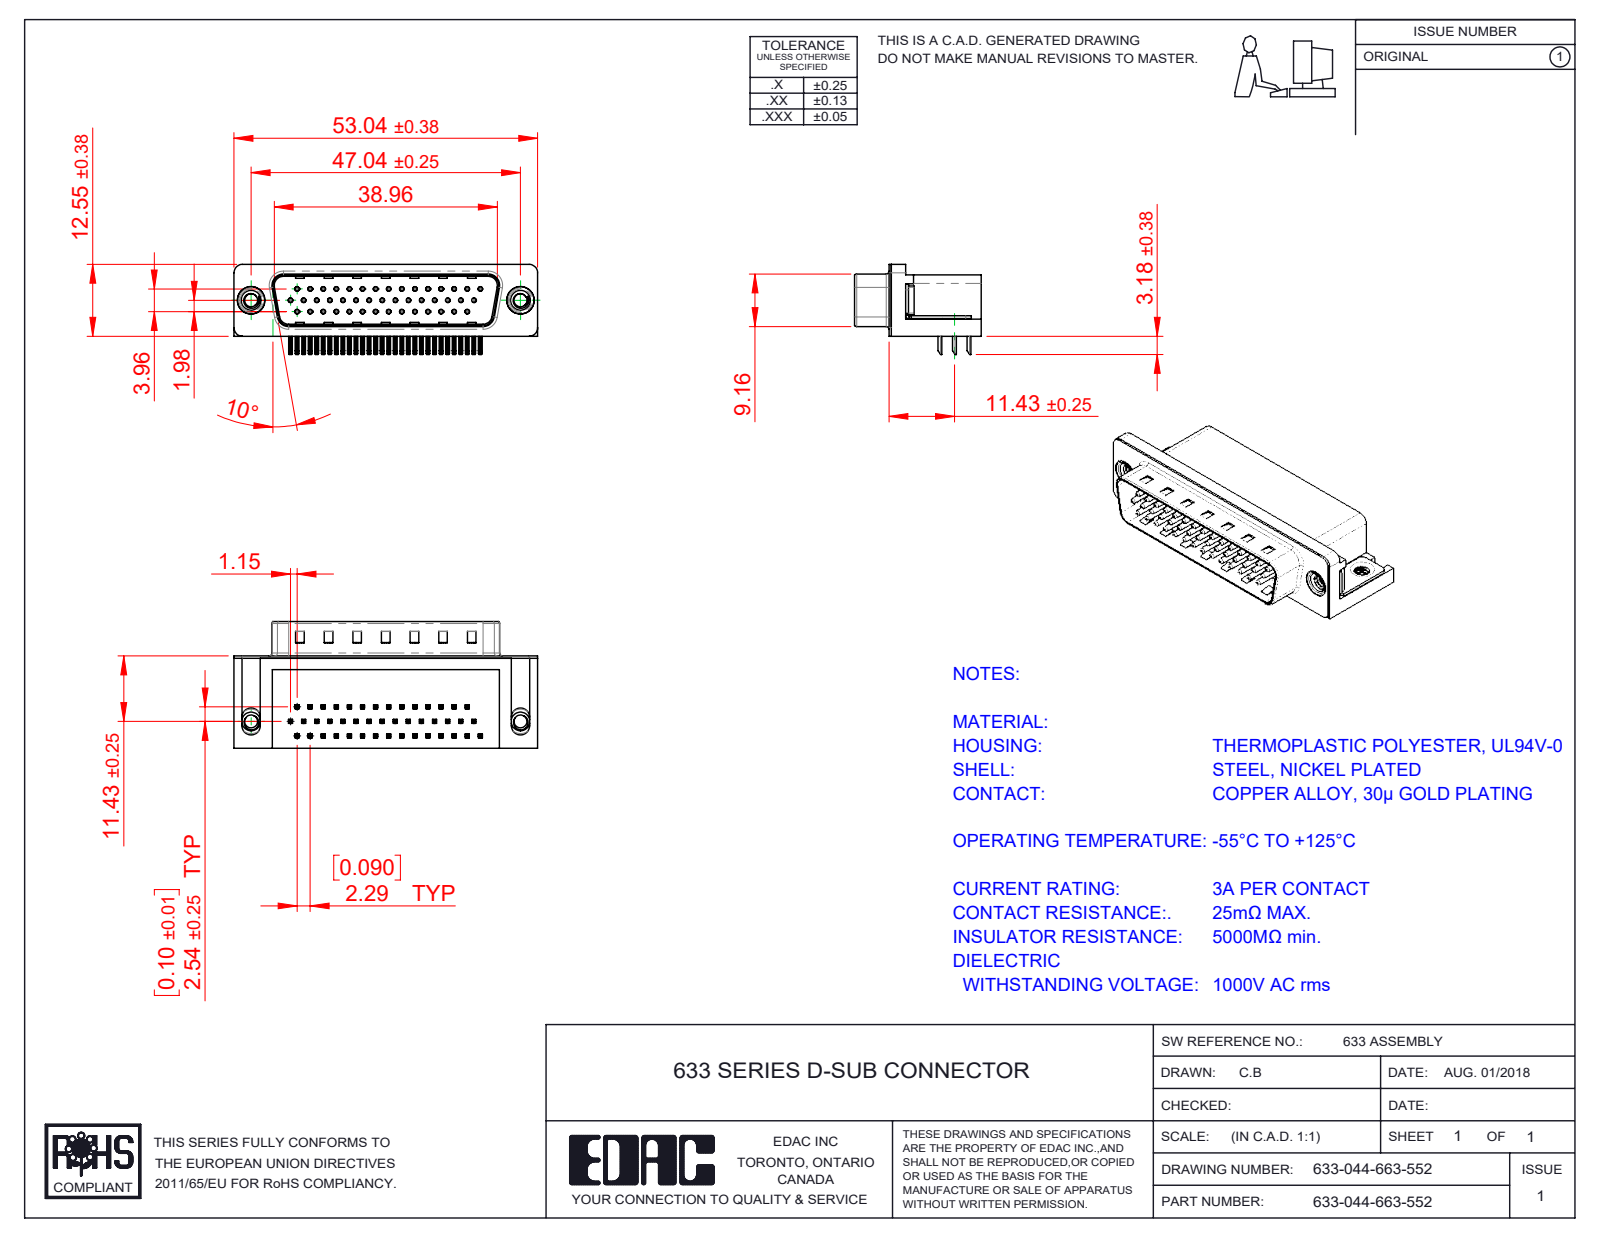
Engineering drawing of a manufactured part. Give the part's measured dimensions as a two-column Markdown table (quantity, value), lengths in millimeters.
| quantity | value |
| --- | --- |
| part name | 633 Contact Top; 633-044-663-552; 633 Contact Middle; 633 Contact Bottom (+4 more) |
| STEP written by | SolidWorks 2016 (CONFIG_CONTROL_DESIGN) |
| units | millimeters |
| bodies | 50 solids, 3810 faces (2359 planar, 1066 cylindrical, 385 other) |
| overall size | 53.04 × 22.1 × 16.25 |
| volume | 8 125 mm³ |
| surface area | 10 293 mm² |
| round holes (diameter × count) | 0.35 × 44, 0.8 × 44, 2 × 2, 2.26 × 2, 4 × 2, 4.8 × 2, 5 × 2 |
| round bosses / shafts (diameter × count) | 0.75 × 44, 4.9 × 2, 4.75 × 2, 3.9 × 2, 3 × 2 |
| partial cylindrical surfaces (radius × count) | 0.25 × 188, 0.12 × 88, 1 × 16, 0.5 × 9, 1.6 × 8, 1.5 × 7, 0.9 × 4, 2 × 4 |
| main face-to-face distances | 0.4, 10.35, 15.7, 2.9, 8.76, 2.5, 2.1, 16.1, 10.7, 2.54 |
| hole center spacings | 2.29, 4.57, 4.58, 2.28, 6.87, 9.16, 11.45, 2.27 |
